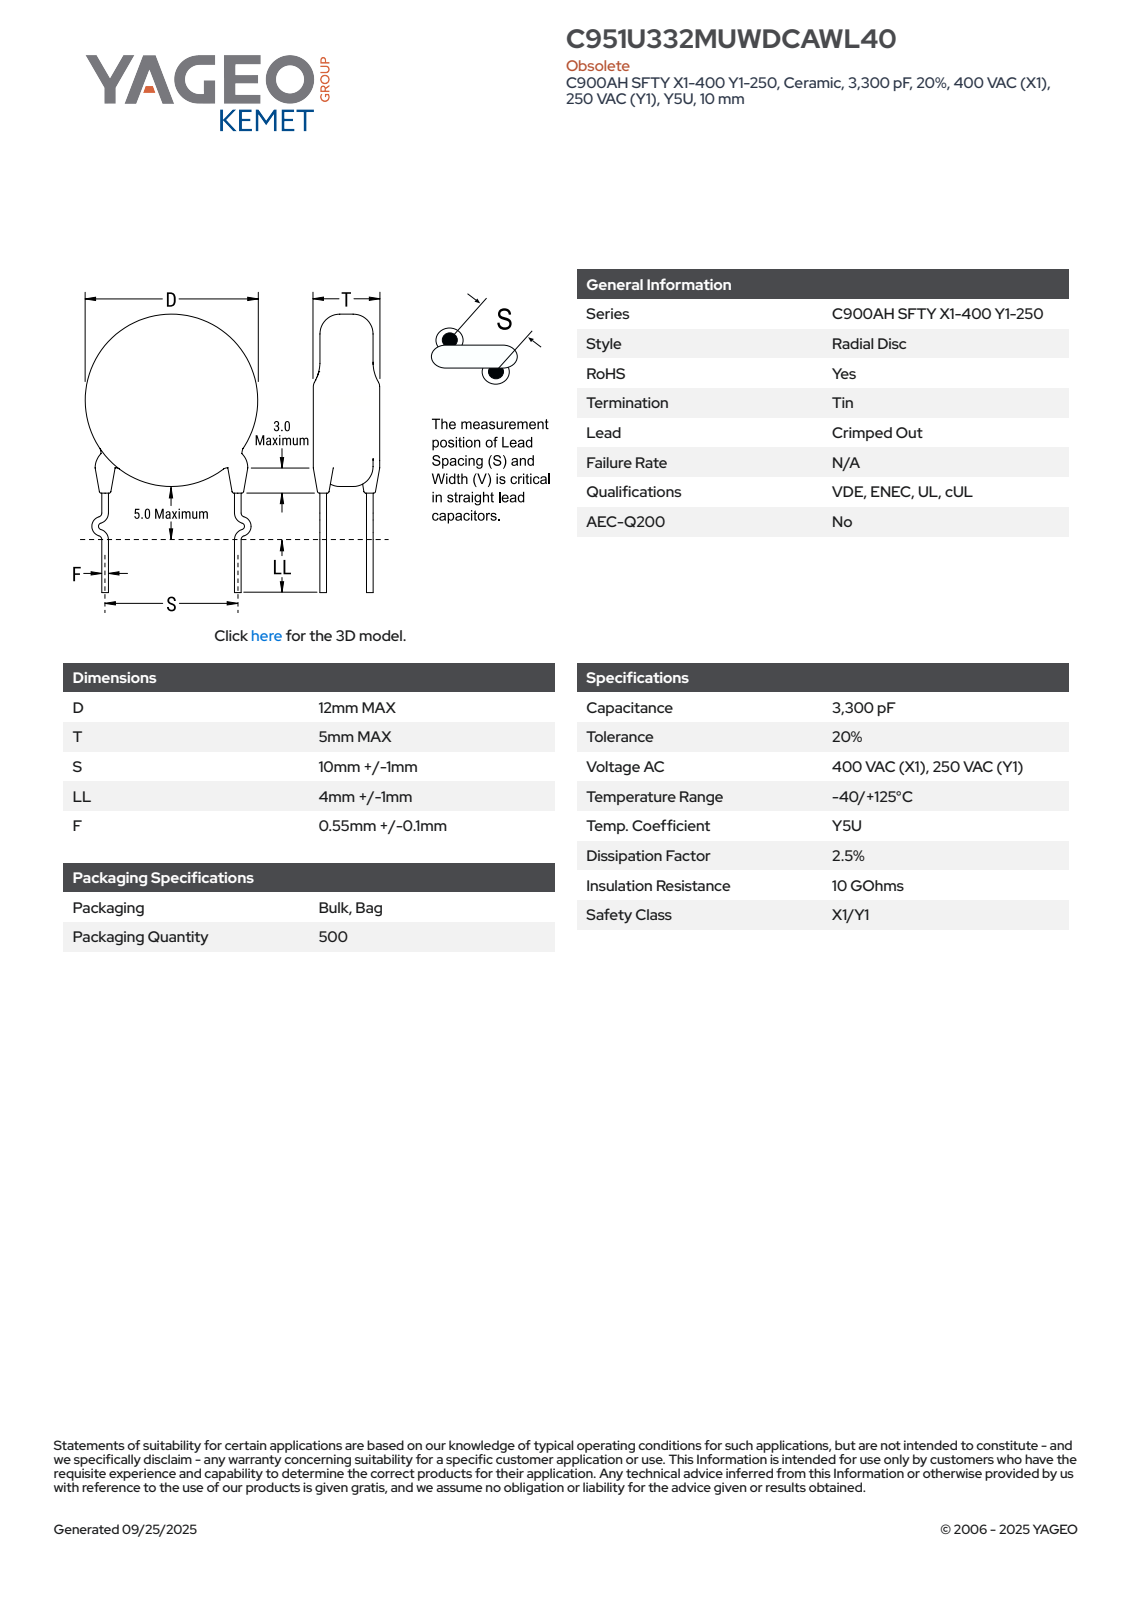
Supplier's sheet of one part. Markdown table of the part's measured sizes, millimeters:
| quantity | value |
| --- | --- |
| part name | CCD_KCOC900_D12T5S10LL5F0.55 |
| STEP written by | SolidWorks 2014 (AUTOMOTIVE_DESIGN) |
| units | millimeters |
| bodies | 4 solids, 85 faces (63 planar, 6 cylindrical, 16 other) |
| overall size | 22 × 14.98 × 5 |
| volume | 564 mm³ |
| surface area | 460 mm² |
| round bosses / shafts (diameter × count) | 1.2 × 2, 12 × 1 |
| main face-to-face distances | 5, 6.63, 5.39, 1.24, 0.34, 5.1, 0.46, 1, 0.45, 2.58 |
